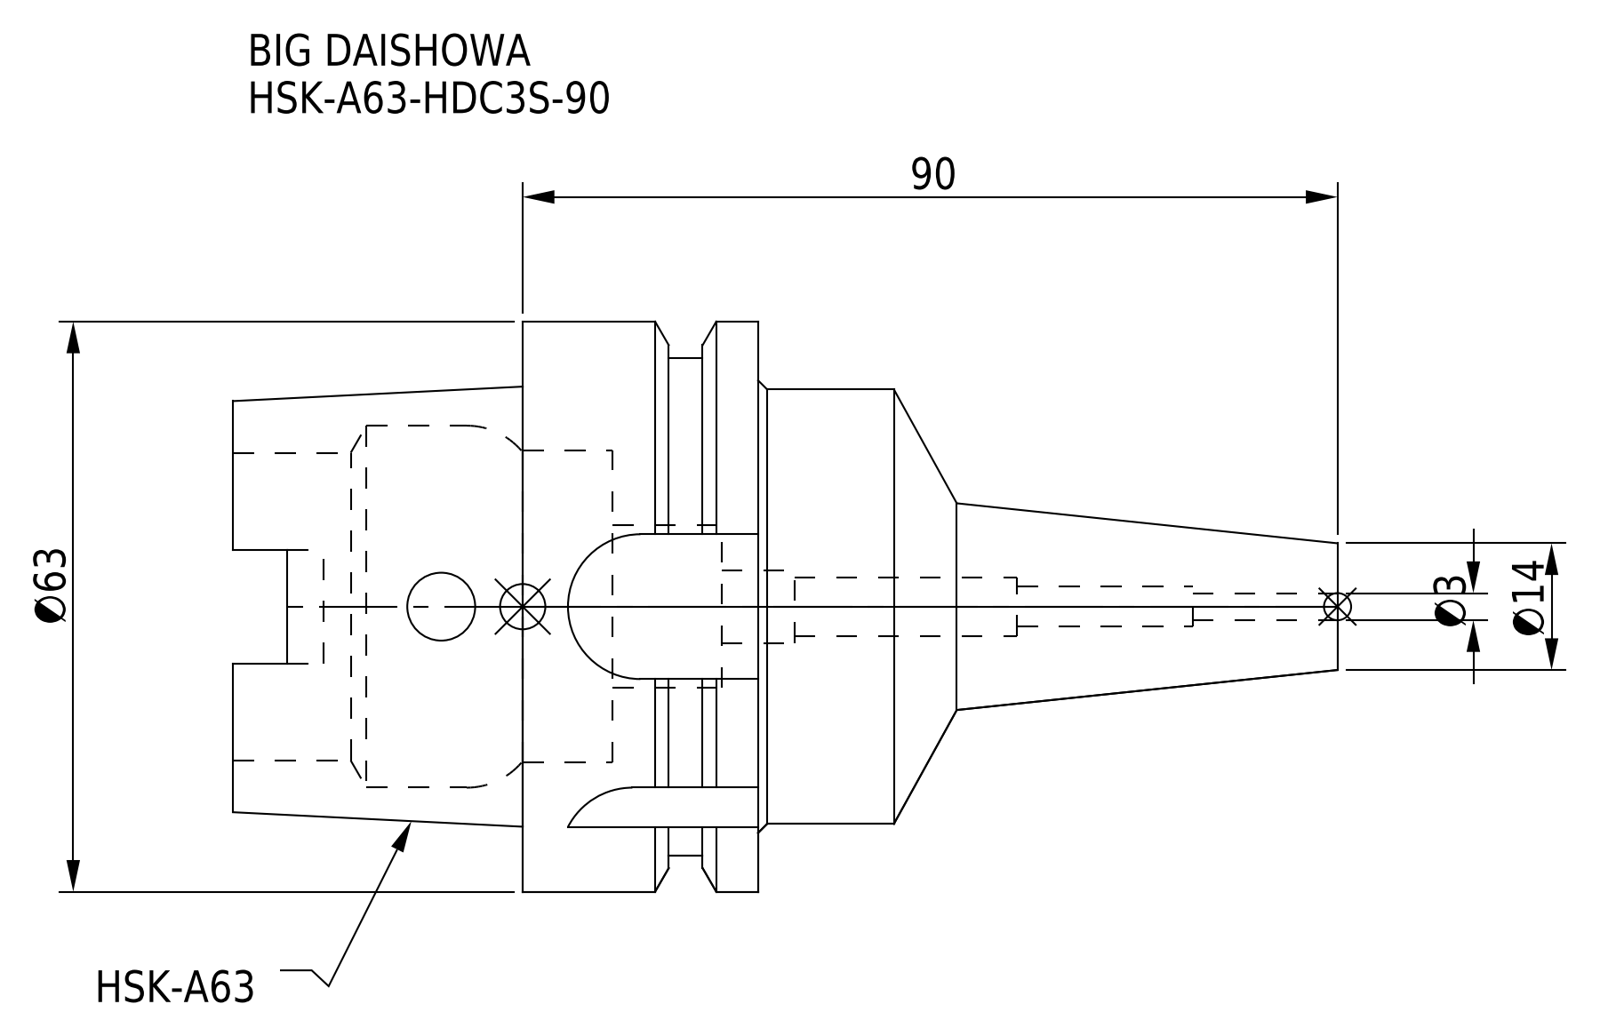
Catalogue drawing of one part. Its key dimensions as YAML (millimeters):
part_name: "HSK-A63-HDC3S-90"
step_written_by: "CREO PARAMETRIC BY PTC INC, 2016380 (AUTOMOTIVE_DESIGN)"
units: millimeters
bodies: {solids: 1, faces: 98, planar: 39, cylindrical: 39, other: 20}
overall_size: [122, 63, 63]
volume: 125968
surface_area: 27991
round_holes:
  - {diameter: 3, count: 1}
  - {diameter: 4.4, count: 1}
  - {diameter: 6.5, count: 1}
  - {diameter: 7.5, count: 1}
  - {diameter: 8, count: 1}
  - {diameter: 18, count: 1}
  - {diameter: 34, count: 1}
  - {diameter: 34.5, count: 1}
  - {diameter: 40, count: 1}
round_bosses_or_shafts:
  - {diameter: 63, count: 1}
  - {diameter: 55, count: 1}
  - {diameter: 48, count: 1}
partial_cylinders:
  - {radius: 2.88, count: 4}
  - {radius: 8, count: 4}
face_to_face_distances: [26, 16.05, 9.95, 58, 41.95, 32, 53, 12, 4.05, 21.95]
